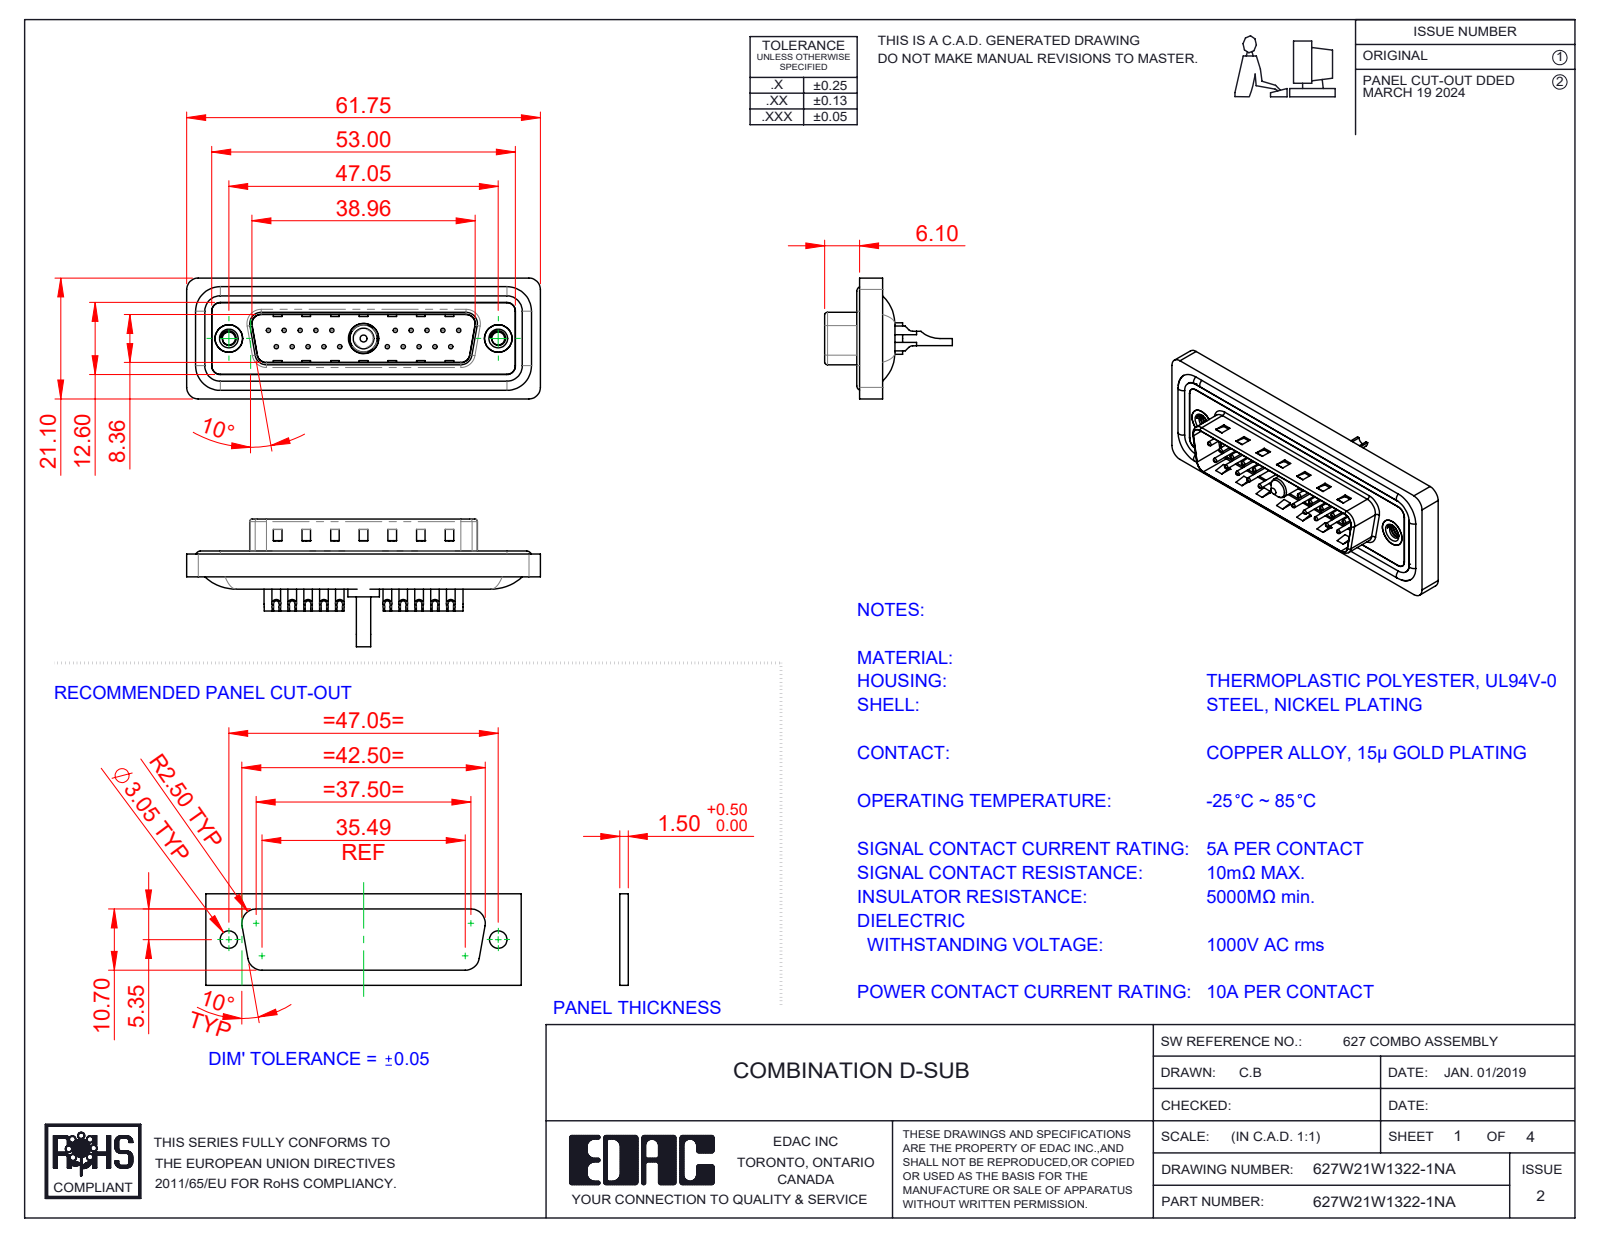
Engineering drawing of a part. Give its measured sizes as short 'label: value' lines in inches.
name: 627Combo Shell Front_25 Contacts; 627Combo Housing_21W1; 627Combo Threaded Rivet_A; 627W21W1322-1NA (+5 more)
written by: SolidWorks 2023 (CONFIG_CONTROL_DESIGN)
unit: in
bodies: 29 solids, 1266 faces (401 planar, 532 cylindrical, 333 other)
size: 2.431 × 0.878 × 0.831
volume: 0.441 in³; area: 18.84 in²
holes: 20× ⌀0.03, 20× ⌀0.039, 20× ⌀0.063, 20× ⌀0.079, 2× ⌀0.089, 2× ⌀0.157, 2× ⌀0.189, 2× ⌀0.197, 1× ⌀0.067, 1× ⌀0.191, 1× ⌀0.209
bosses: 20× ⌀0.059, 4× ⌀0.063, 2× ⌀0.193, 1× ⌀0.217, 1× ⌀0.205, 1× ⌀0.187, 1× ⌀0.148, 1× ⌀0.142
rounds: 22× R0.059, 18× R0.079, 8× R0.02, 8× R0.063, 6× R0.039, 4× R0.01, 4× R0.024, 4× R0.026
face distances: 0.016, 0.059, 0.043, 0.063, 0.02, 0.122, 0.114, 0.161, 0.032, 0.377
hole spacings: 0.124, 0.109, 0.218, 0.327, 0.198, 0.763, 0.826, 0.872
